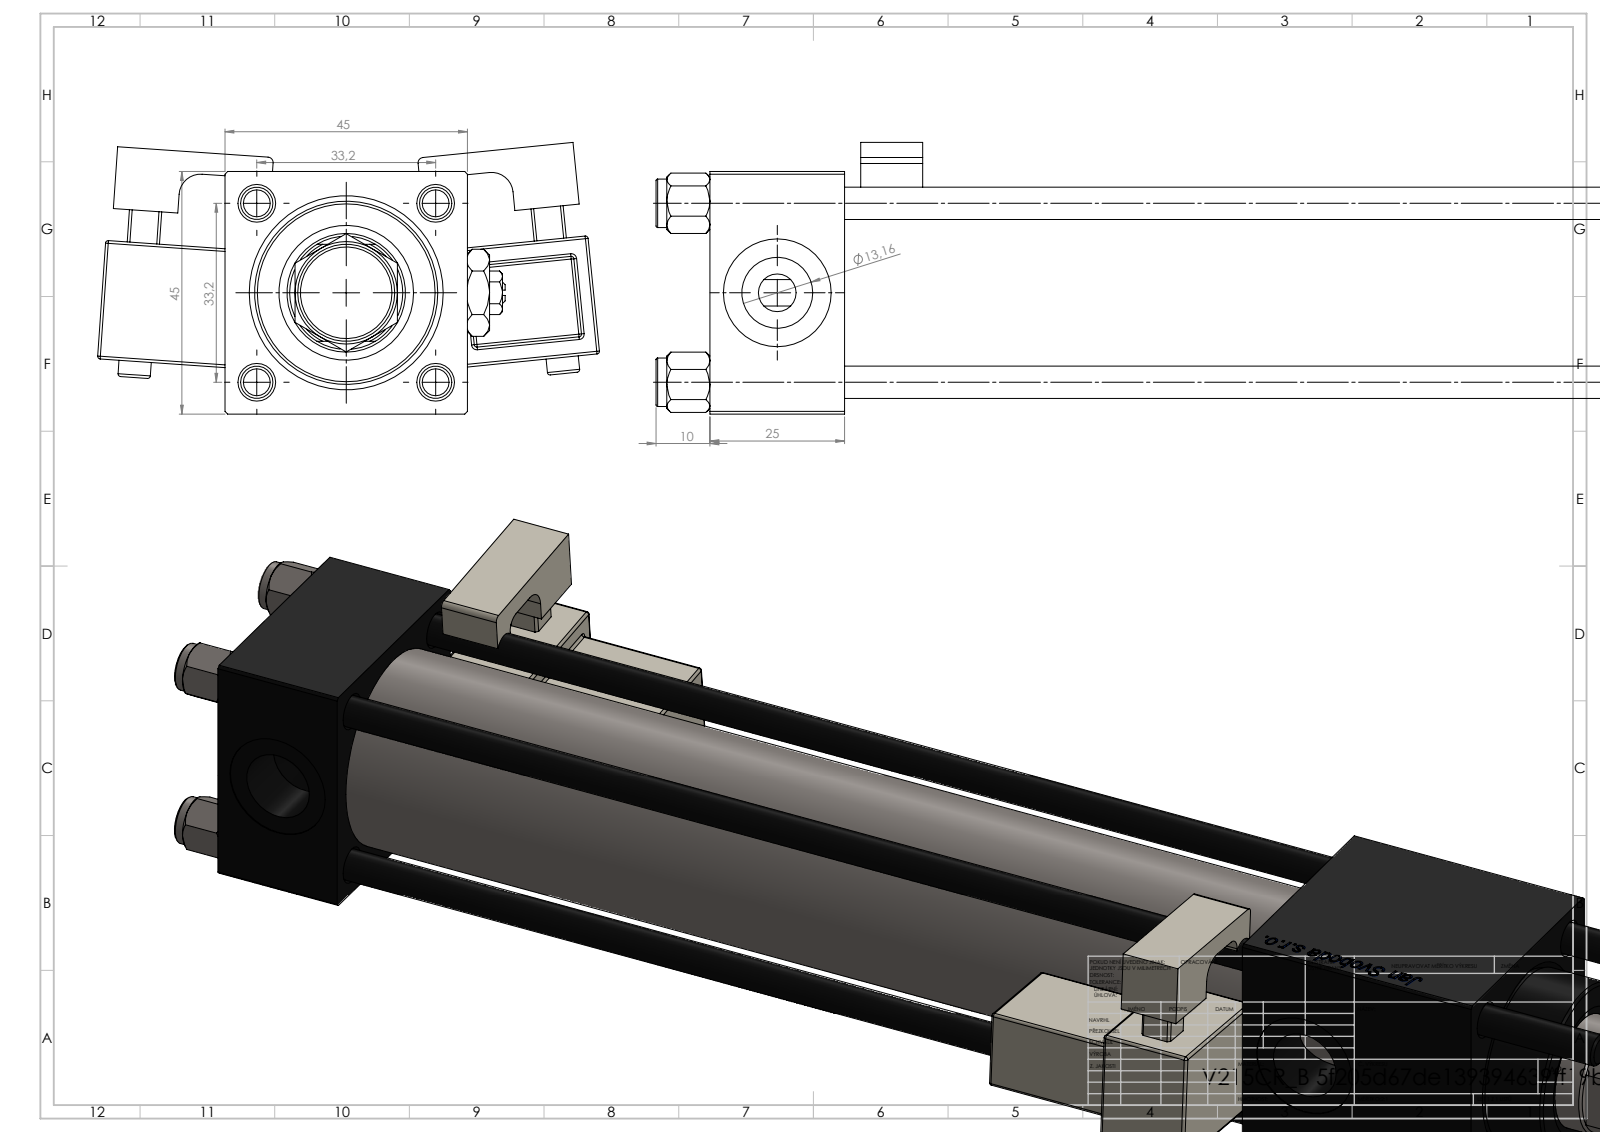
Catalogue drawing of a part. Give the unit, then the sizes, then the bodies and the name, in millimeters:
Units: millimetres
Overall size (bounding box): 331 × 93.14 × 50.4
Round holes (diameter × count): ⌀6 ×4, ⌀7 ×2, ⌀13.16 ×2, ⌀20 ×2, ⌀10.5 ×1, ⌀22 ×1, ⌀24 ×1, ⌀25 ×1, ⌀32 ×1, ⌀33 ×1
Round bosses / shafts (diameter × count): ⌀9 ×4, ⌀6 ×2, ⌀38 ×1, ⌀34 ×1, ⌀18 ×1, ⌀11 ×1
Partial cylindrical surfaces — rounded edges, fillets, slot ends (radius × count): R0.5 ×48, R1 ×2, R2.5 ×2, R4 ×2, R10.5 ×1
Main face-to-face distances: 45, 25, 215, 190, 263, 3, 172.5, 17.5, 44.8, 39.5
Hole centre spacings: 23.48, 33.2, 46.95, 215.5
Volume: 376 740 mm³ · Surface area: 144 347 mm²
Bodies: 16 solids, 1466 faces (556 planar, 152 cylindrical, 758 other)
Part name (STEP PRODUCT): V215CR_MSU; V215CR_VCP_B; V215CR_B-1; NUT_M5_B (+4 more)
STEP written by: SolidWorks 2019 (CONFIG_CONTROL_DESIGN)
